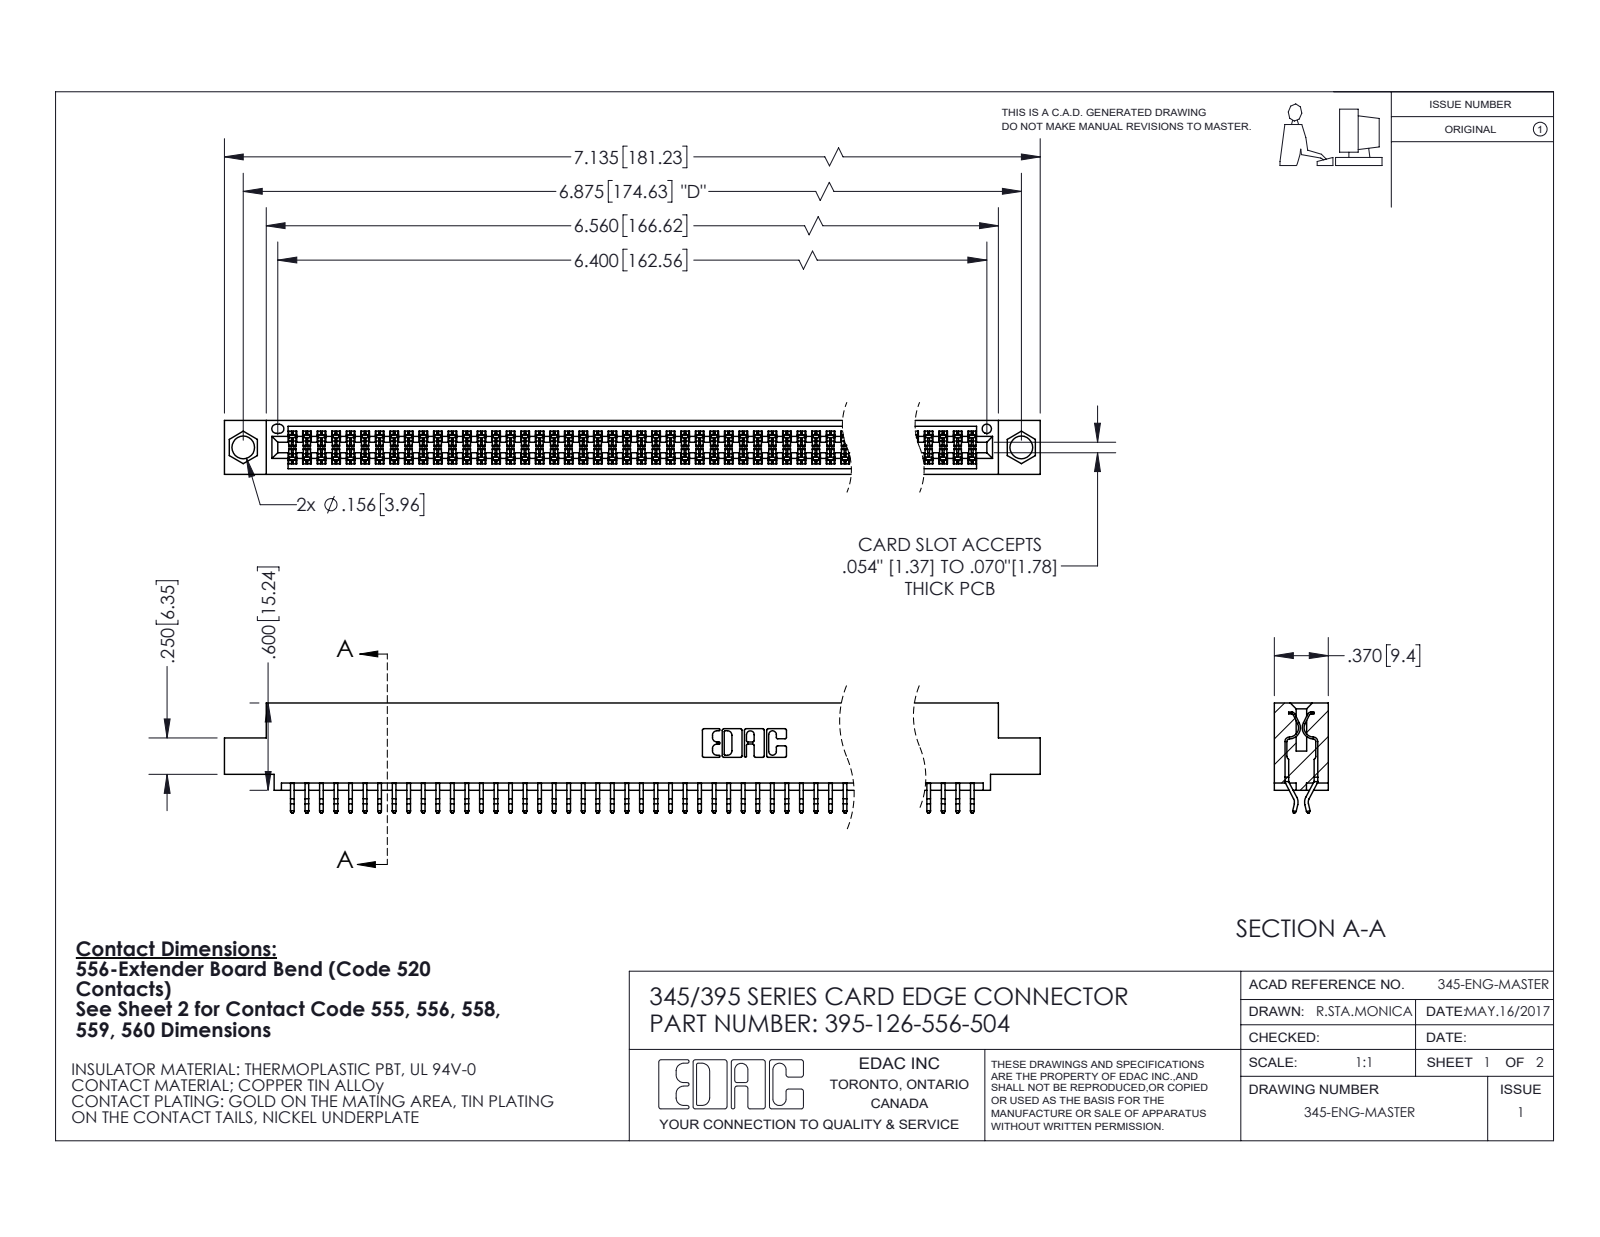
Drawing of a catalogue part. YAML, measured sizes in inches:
part_name: "345-292-001_556 Tail; 395-126-556-504; 345 Part_0.110 Offset - 0.156 Dia-TI"
step_written_by: "SolidWorks 2020 (CONFIG_CONTROL_DESIGN)"
units: inches
bodies: {solids: 127, faces: 7200, planar: 4760, cylindrical: 2440, other: 0}
overall_size: [7.135, 0.757, 0.37]
volume: 1.075
surface_area: 40.73
round_holes:
  - {diameter: 0.156, count: 2}
  - {diameter: 0.064, count: 1}
partial_cylinders:
  - {radius: 0.006, count: 252}
  - {radius: 0.01, count: 22}
  - {radius: 0.007, count: 6}
  - {radius: 0.031, count: 6}
  - {radius: 0.026, count: 3}
  - {radius: 0.01, count: 2}
  - {radius: 0.014, count: 2}
  - {radius: 0.019, count: 2}
face_to_face_distances: [0.298, 0.072, 0.37, 0.2, 0.025, 0.098, 0.272, 0.225, 0.175, 0.149]
hole_center_spacings: [0.27, 6.639, 6.875]
